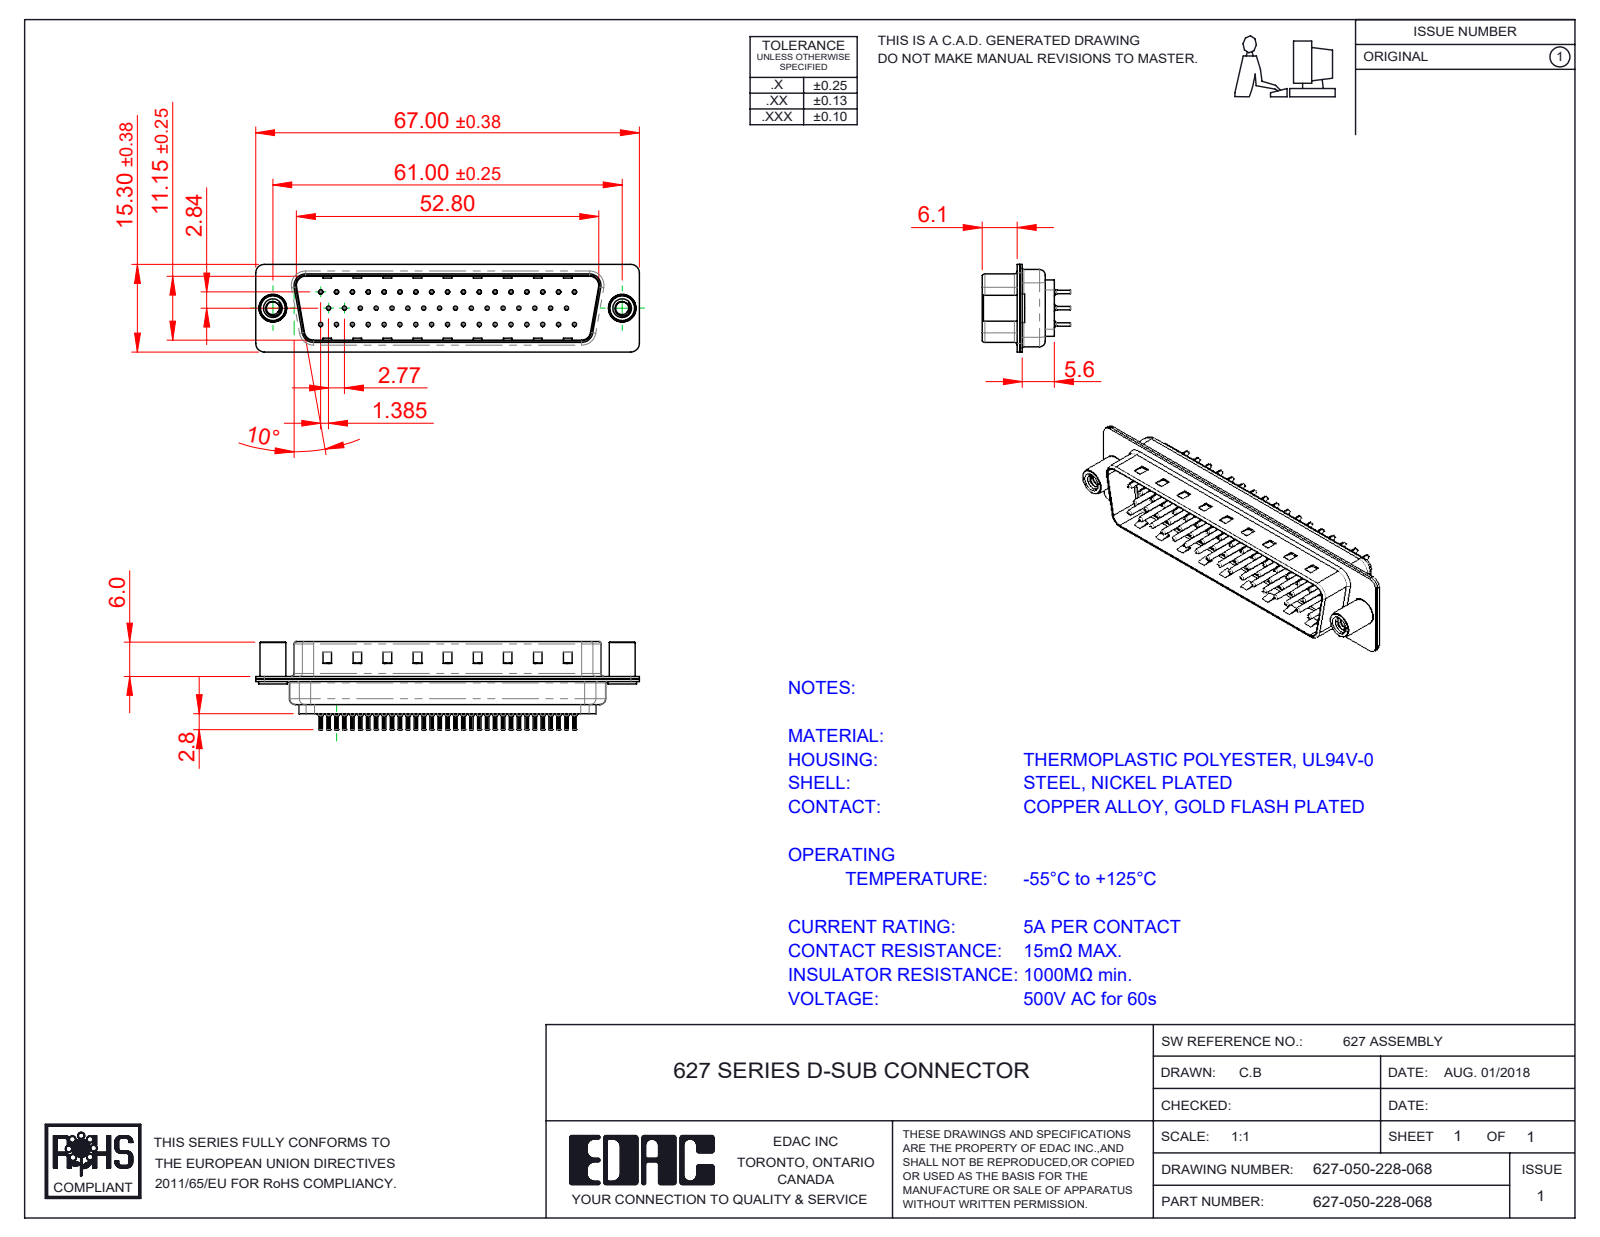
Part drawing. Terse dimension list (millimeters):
name: 627 4-40 Threaded Standoff; 627 Contact Row 2_28L; 627 Housing_50 FF; 627 Shell Front_50 Contacts (+4 more)
written by: SolidWorks 2020 (CONFIG_CONTROL_DESIGN)
unit: mm
bodies: 56 solids, 5457 faces (1411 planar, 2124 cylindrical, 1922 other)
size: 67 × 18.8 × 15.3
volume: 5 618 mm³; area: 14 825 mm²
holes: 50× ⌀0.2, 50× ⌀0.35, 50× ⌀1.1, 50× ⌀1.6, 2× ⌀2.26, 2× ⌀4, 2× ⌀4.8
bosses: 50× ⌀2, 50× ⌀1.5, 50× ⌀0.75, 50× ⌀0.6, 2× ⌀5, 2× ⌀4.9, 2× ⌀4.5
rounds: 100× R0.1, 16× R1.5, 12× R2, 8× R0.5, 8× R1.6, 4× R0.25, 4× R0.6, 4× R0.65
face distances: 0.4, 6.05, 0.45, 11.55, 0.9, 2.8, 8.85, 9.3, 6.5, 0.78
hole spacings: 2.77, 3.16, 5.54, 8.31, 11.08, 13.85, 16.62, 19.39
